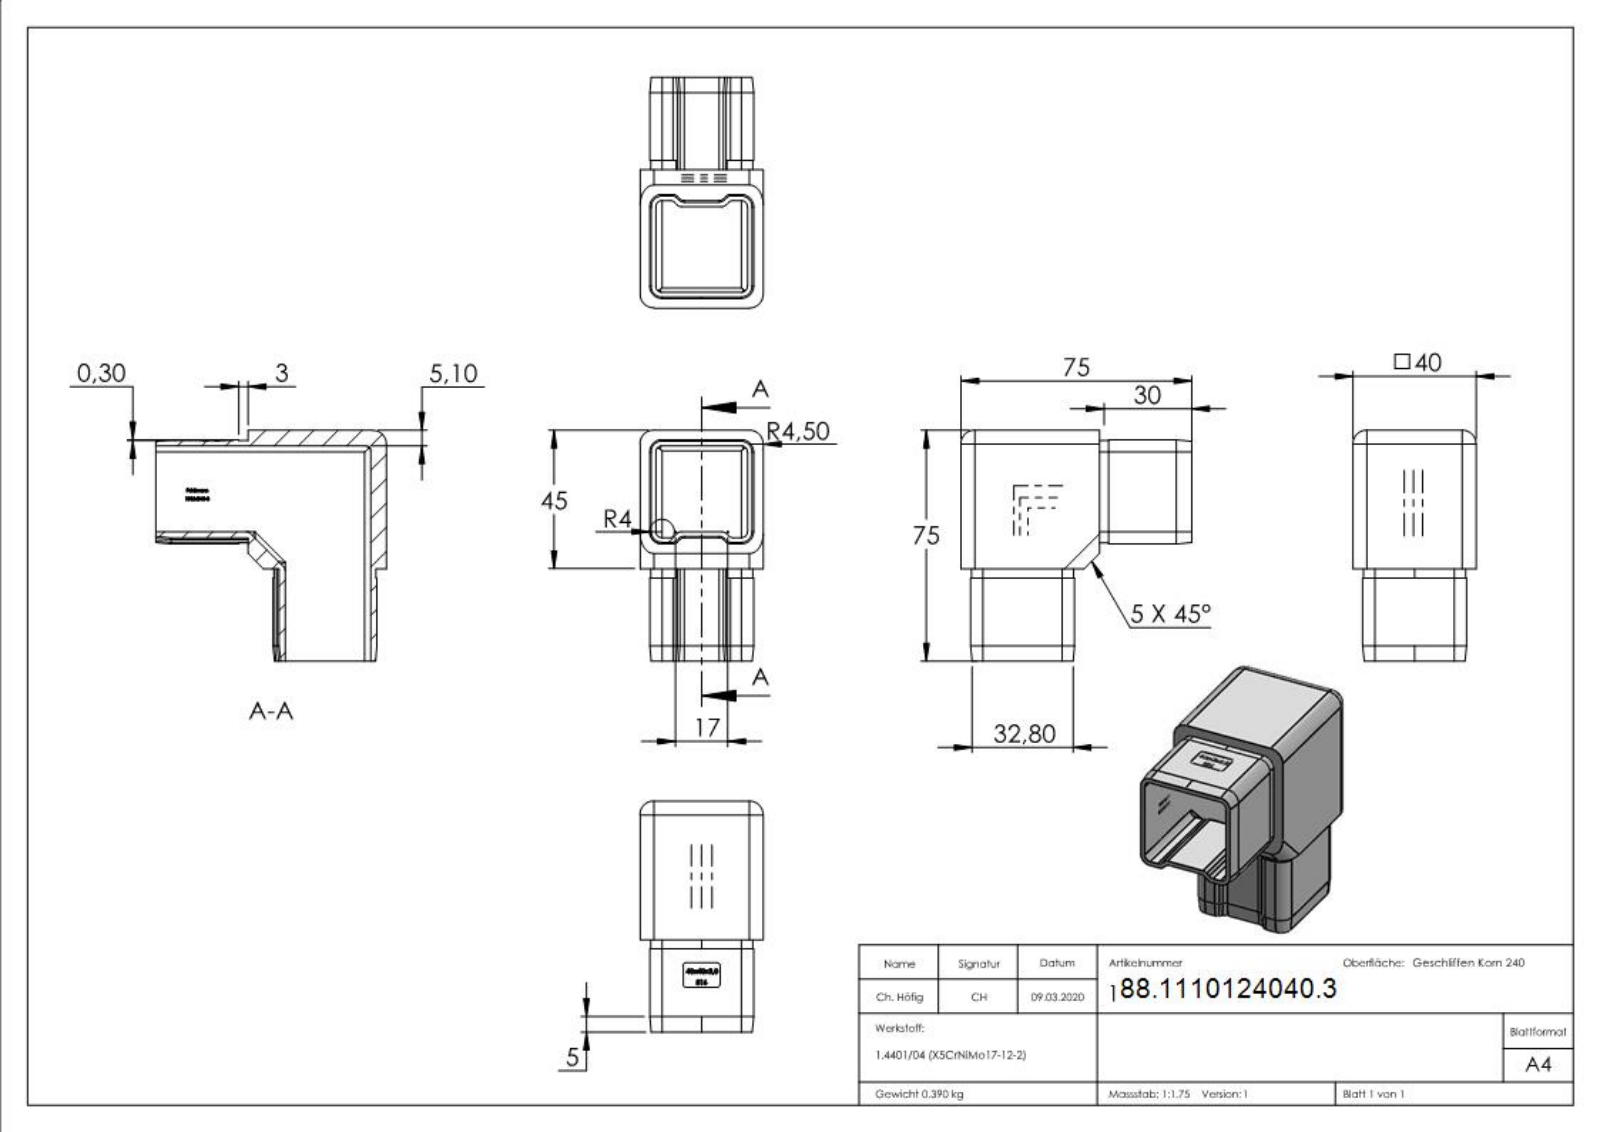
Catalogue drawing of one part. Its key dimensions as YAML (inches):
part_name: "10124040-3"
step_written_by: "SolidWorks 2015 (CONFIG_CONTROL_DESIGN)"
units: inches
bodies: {solids: 1, faces: 574, planar: 315, cylindrical: 64, other: 195}
overall_size: [2.953, 2.953, 1.575]
volume: 2.972
surface_area: 45.65
partial_cylinders:
  - {radius: 0.079, count: 24}
  - {radius: 0.059, count: 11}
  - {radius: 0.146, count: 8}
  - {radius: 0.157, count: 8}
  - {radius: 0.177, count: 7}
  - {radius: 0.039, count: 4}
face_to_face_distances: [0.201, 1.173, 0.079, 1.374, 1.252, 0.122, 1.453, 1.575, 1.331, 1.571]
